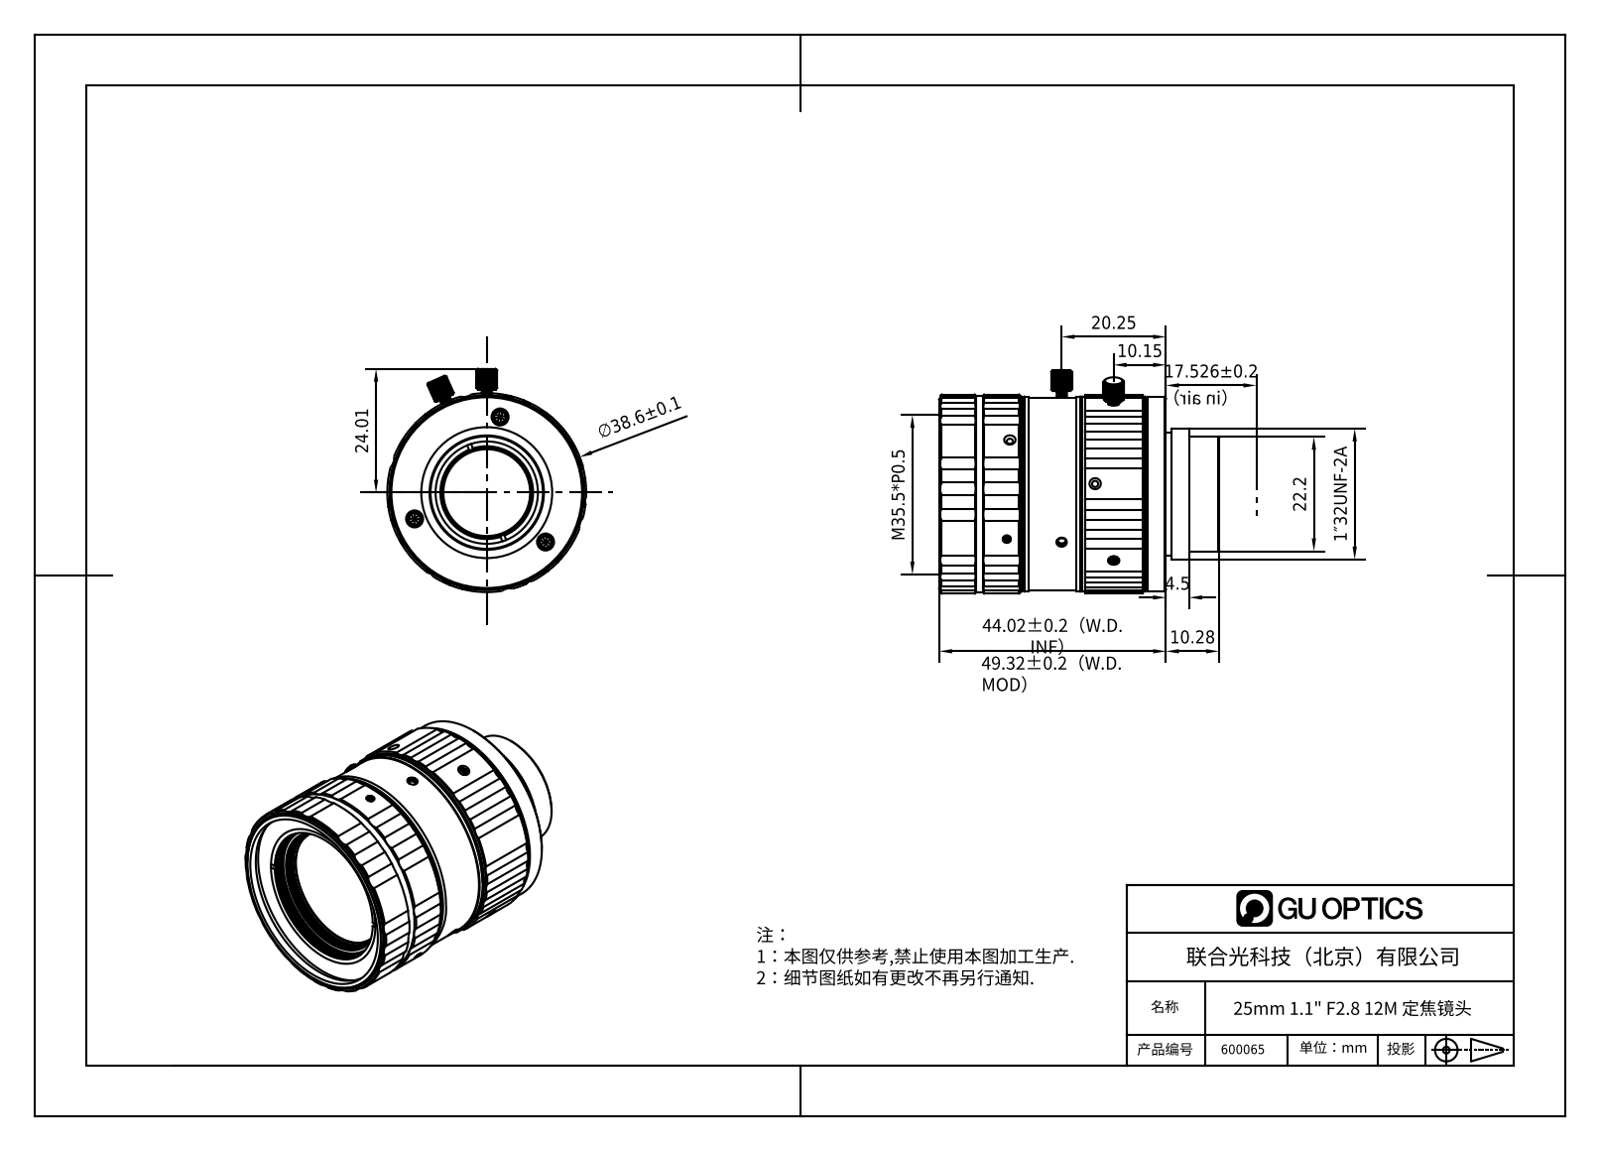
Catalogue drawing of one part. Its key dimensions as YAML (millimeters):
part_name: "600065"
step_written_by: "SolidWorks 2020 (CONFIG_CONTROL_DESIGN)"
units: millimeters
bodies: {solids: 12, faces: 1331, planar: 307, cylindrical: 689, other: 335}
overall_size: [54.3, 43.4, 38.6]
volume: 49828
surface_area: 14910
round_holes:
  - {diameter: 1.6, count: 10}
  - {diameter: 2, count: 8}
  - {diameter: 1.2, count: 3}
  - {diameter: 1.8, count: 3}
  - {diameter: 2.9, count: 3}
  - {diameter: 17.6, count: 1}
  - {diameter: 19.86, count: 1}
  - {diameter: 23.51, count: 1}
  - {diameter: 24.8, count: 1}
  - {diameter: 26.16, count: 1}
  - {diameter: 26.9, count: 1}
  - {diameter: 26.9, count: 1}
round_bosses_or_shafts:
  - {diameter: 1.6, count: 9}
  - {diameter: 2.5, count: 4}
  - {diameter: 1.25, count: 3}
  - {diameter: 1.2, count: 3}
  - {diameter: 2, count: 2}
  - {diameter: 38.6, count: 1}
  - {diameter: 38, count: 1}
  - {diameter: 37.8, count: 1}
partial_cylinders:
  - {radius: 2, count: 26}
  - {radius: 3, count: 18}
  - {radius: 0.15, count: 12}
  - {radius: 0.42, count: 12}
  - {radius: 1.11, count: 6}
  - {radius: 3.39, count: 6}
  - {radius: 3.43, count: 6}
  - {radius: 1, count: 3}
face_to_face_distances: [41.52, 2.11, 39.35, 2.17, 2, 4.5, 43.85, 46.02, 41.74, 37.24]
hole_center_spacings: [14.9, 25.81, 10.1, 25.8]
